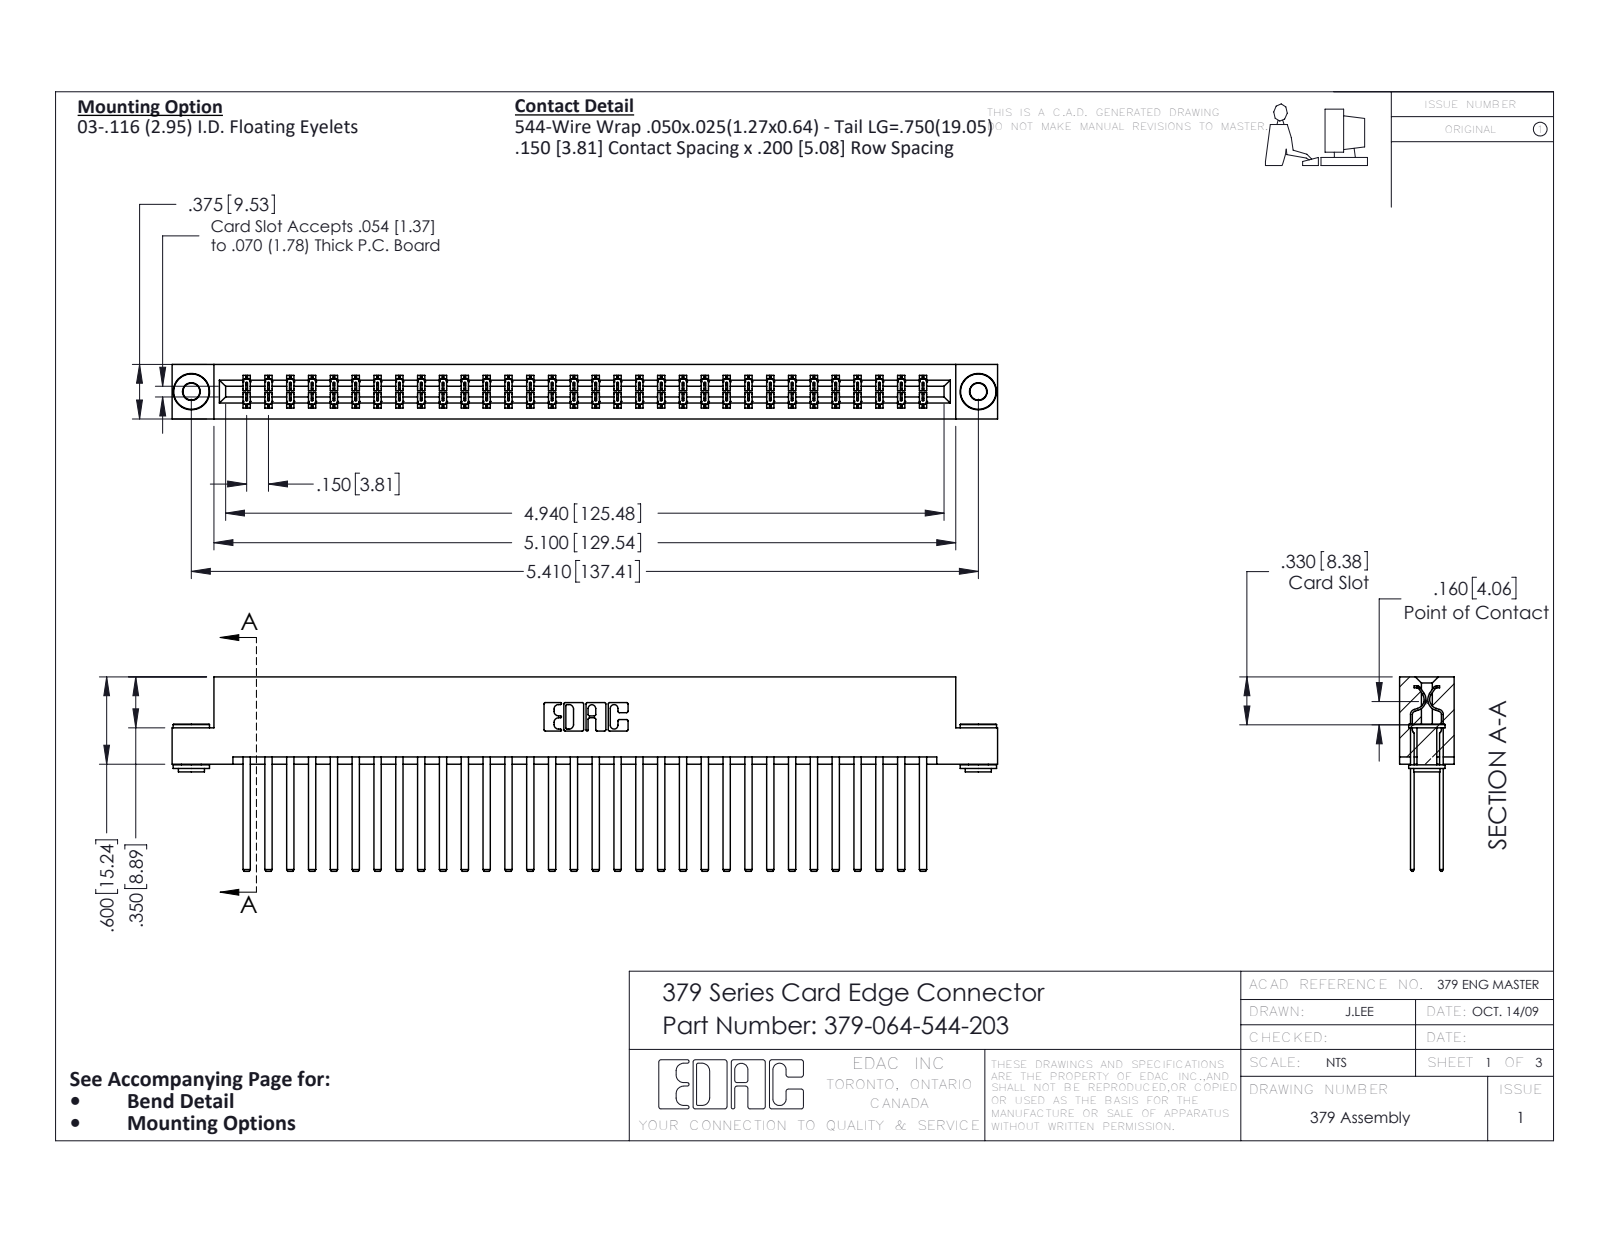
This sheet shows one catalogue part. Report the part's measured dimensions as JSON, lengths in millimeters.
{"part_name": "379 Part_Flush - .156 Dia - TH; 345-250-002_345-250-002-102; 379-064-544-203; 345-292-001_345-293-144", "step_written_by": "SolidWorks 2016 (CONFIG_CONTROL_DESIGN)", "units": "millimeters", "bodies": {"solids": 67, "faces": 3096, "planar": 2128, "cylindrical": 960, "other": 8}, "overall_size": [144.1, 34, 9.5], "volume_mm3": 16200, "surface_area_mm2": 21210, "round_holes": [[2.9, 2], [4, 2]], "round_bosses_or_shafts": [[6.4, 2], [4.6, 2], [3.5, 2]], "partial_cylinders_radius": [[0.2, 96], [0.3, 22], [0.2, 6], [0.8, 6], [0.7, 3], [0.4, 2], [0.6, 2], [0.6, 2]], "face_to_face_distances": [7.6, 2.5, 1.9, 5.1, 7, 9.5, 0.6, 1.9, 3.8, 3.8], "hole_center_spacings": [137.4]}
